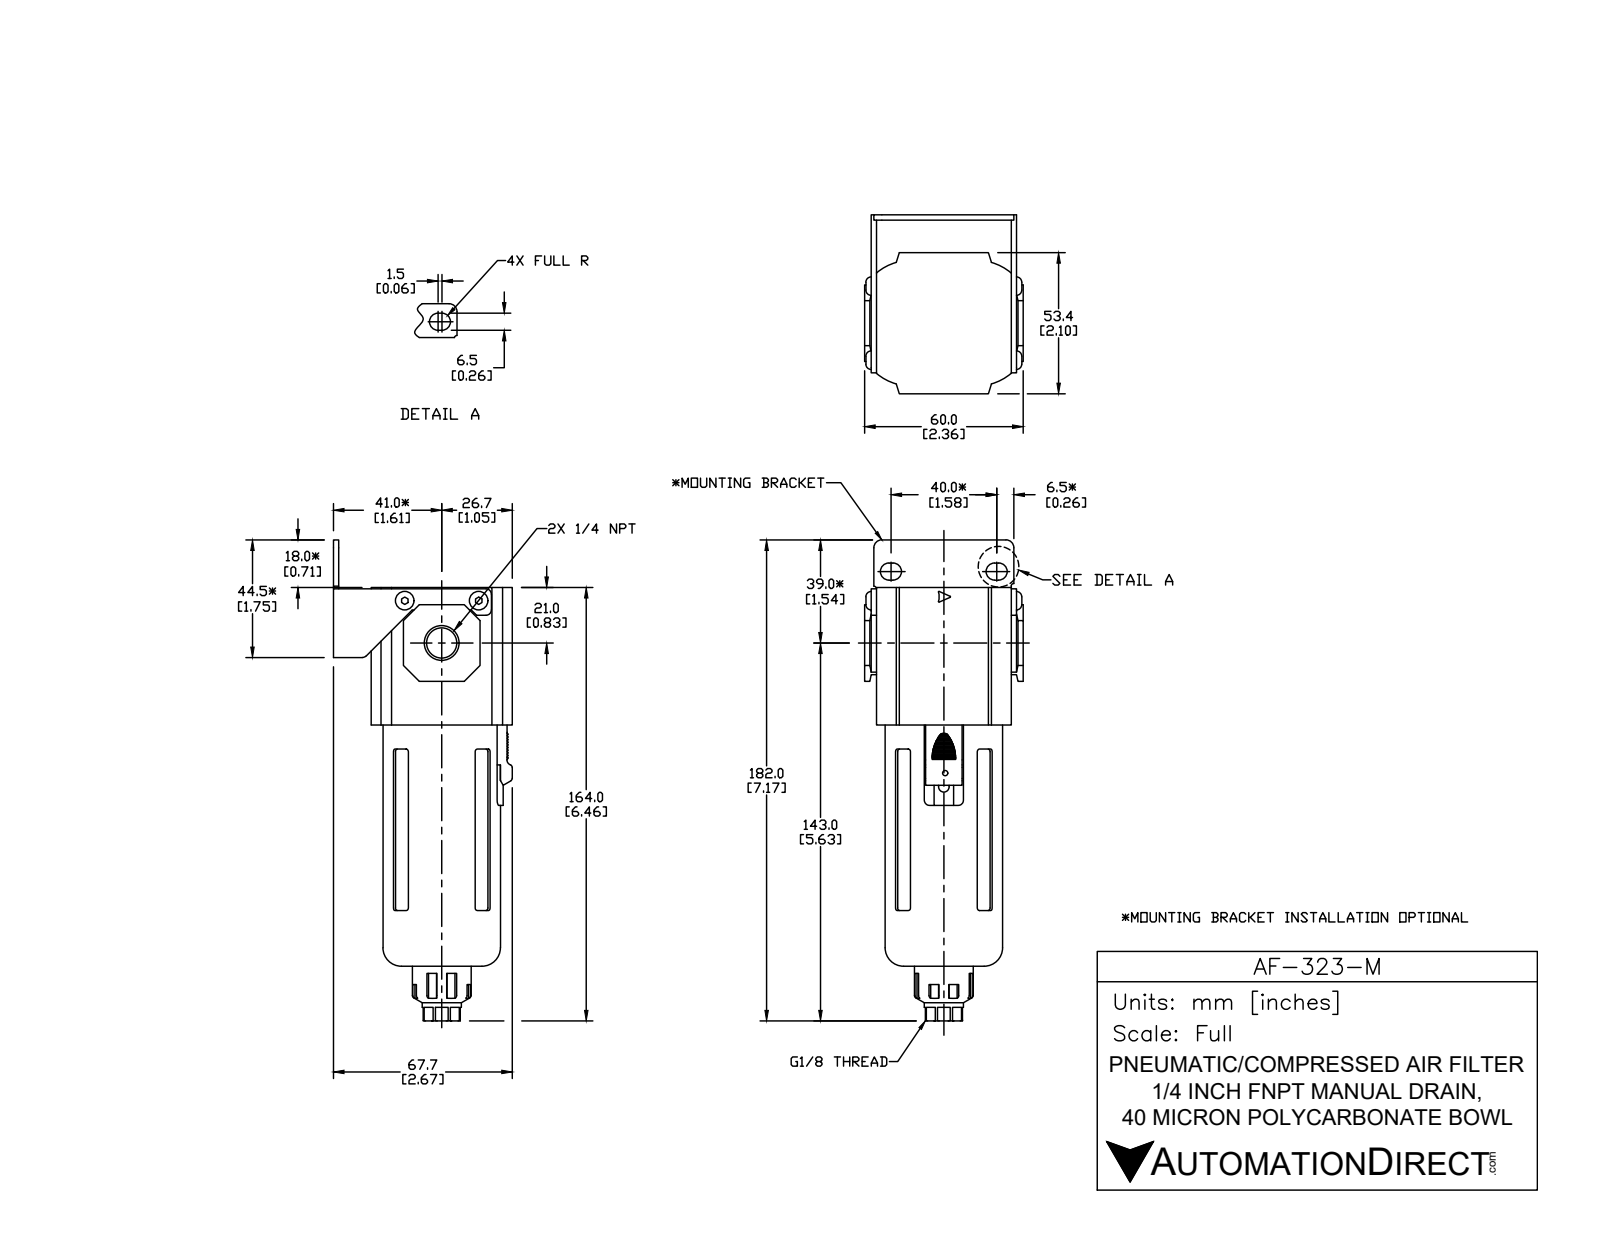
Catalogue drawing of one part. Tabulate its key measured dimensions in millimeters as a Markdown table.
| quantity | value |
| --- | --- |
| part name | AF-323-M |
| STEP written by | SolidWorks 2015 (CONFIG_CONTROL_DESIGN) |
| units | millimeters |
| bodies | 9 solids, 394 faces (246 planar, 94 cylindrical, 54 other) |
| overall size | 182.3 × 67.7 × 60 |
| volume | 206 172 mm³ |
| surface area | 60 550 mm² |
| round holes (diameter × count) | 3.4 × 2, 8.57 × 1, 11.13 × 1, 35.99 × 1, 44.8 × 1 |
| round bosses / shafts (diameter × count) | 44.47 × 1, 26 × 1, 22.24 × 1, 14.82 × 1 |
| partial cylindrical surfaces (radius × count) | 1 × 18, 2 × 8, 9.5 × 8, 0.5 × 6, 0.3 × 4, 3.25 × 4, 20 × 4, 0.2 × 3 |
| main face-to-face distances | 2, 51, 2.5, 53, 12.3, 67.7, 65.7, 14.3, 53.4, 55.5 |
| hole center spacings | 21.06, 21.46, 28 |
